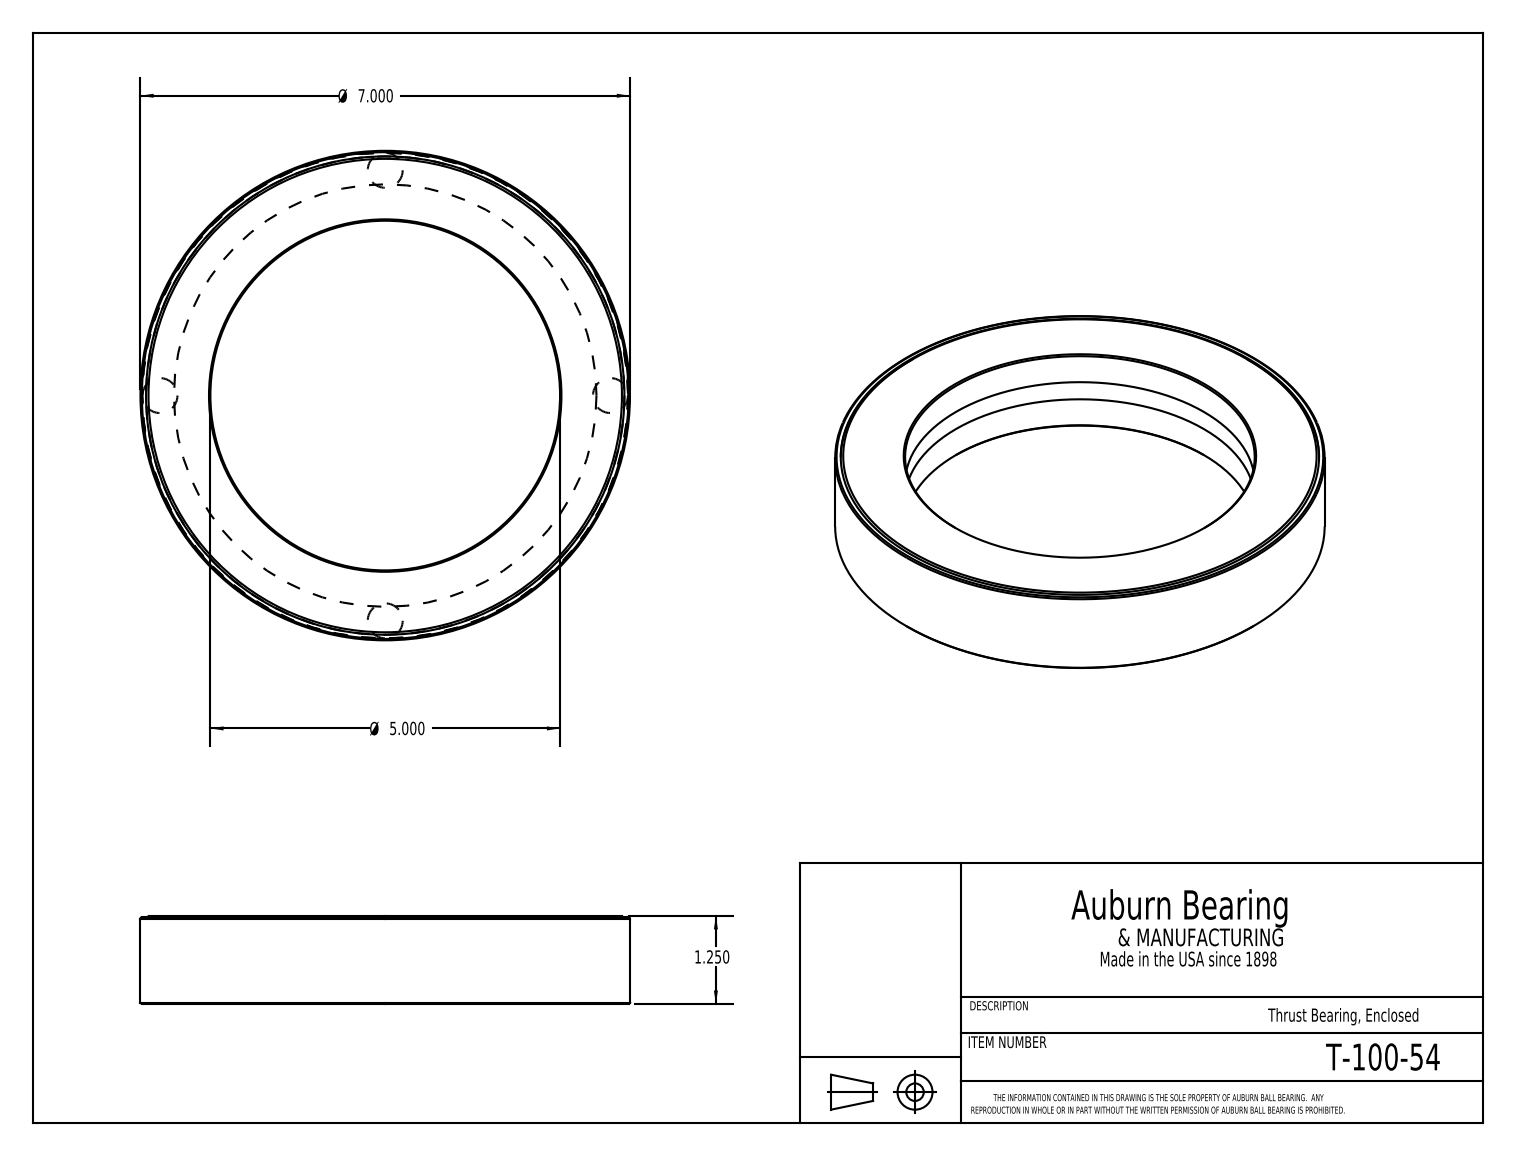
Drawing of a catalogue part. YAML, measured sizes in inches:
part_name: "T-100-54"
step_written_by: "SolidWorks 2016 (CONFIG_CONTROL_DESIGN)"
units: inches
bodies: {solids: 6, faces: 28, planar: 9, cylindrical: 7, other: 12}
overall_size: [7, 7, 1.25]
volume: 17.02
surface_area: 149.9
round_holes:
  - {diameter: 5, count: 1}
  - {diameter: 6.84, count: 1}
  - {diameter: 6.96, count: 1}
round_bosses_or_shafts:
  - {diameter: 7, count: 1}
  - {diameter: 6.946, count: 1}
face_to_face_distances: [0.475, 0.775, 1.25, 0.3, 1.215, 1.235, 0.74, 0.76, 0.44, 0.46]
